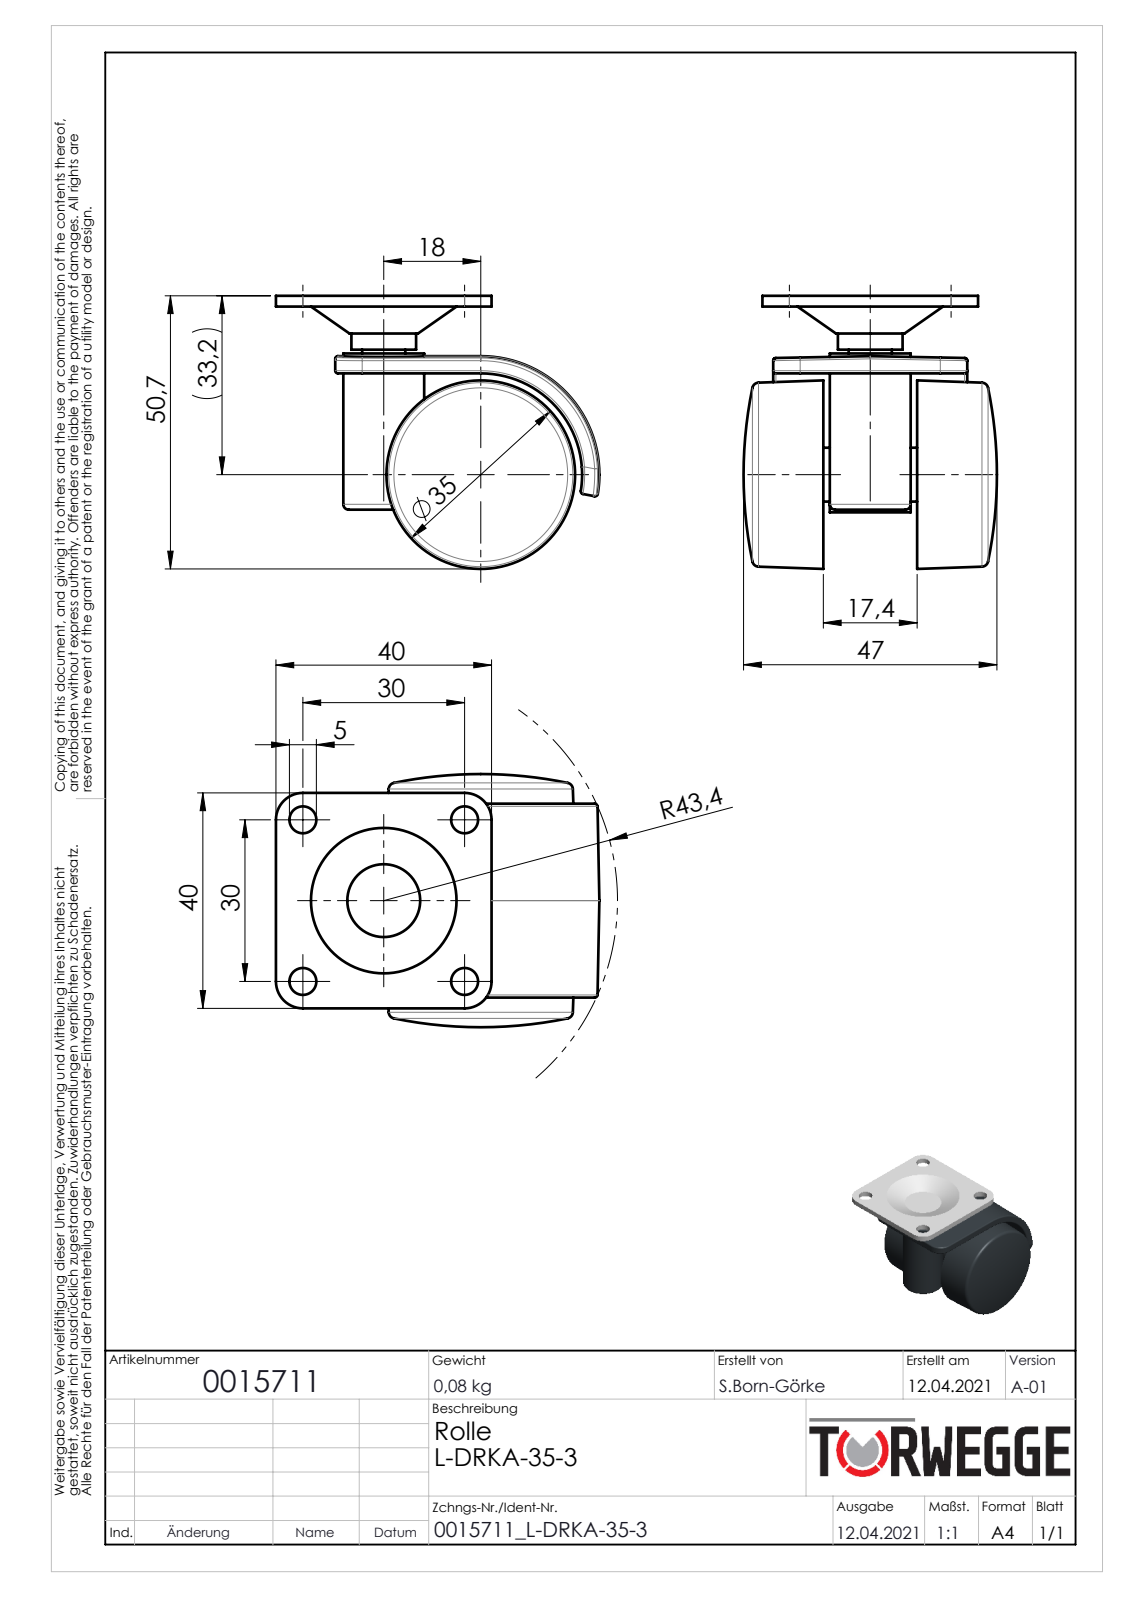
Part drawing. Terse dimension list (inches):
name: 0015711
written by: SolidWorks 2020 (AUTOMOTIVE_DESIGN)
unit: in
bodies: 6 solids, 171 faces (31 planar, 64 cylindrical, 76 other)
size: 2.362 × 1.996 × 1.85
volume: 2.553 in³; area: 30.43 in²
holes: 4× ⌀0.197, 1× ⌀0.118, 1× ⌀0.276, 1× ⌀0.321, 1× ⌀0.323
bosses: 1× ⌀0.591, 1× ⌀0.551, 1× ⌀0.472, 1× ⌀0.394, 1× ⌀0.315
rounds: 8× R0.02, 8× R0.197, 1× R0.039, 1× R0.74
face distances: 0.079, 0.685, 0.488, 0.567, 0.047, 0.638, 0.366, 0.413, 1.004, 1.051
hole spacings: 0.835, 1.181, 1.67
